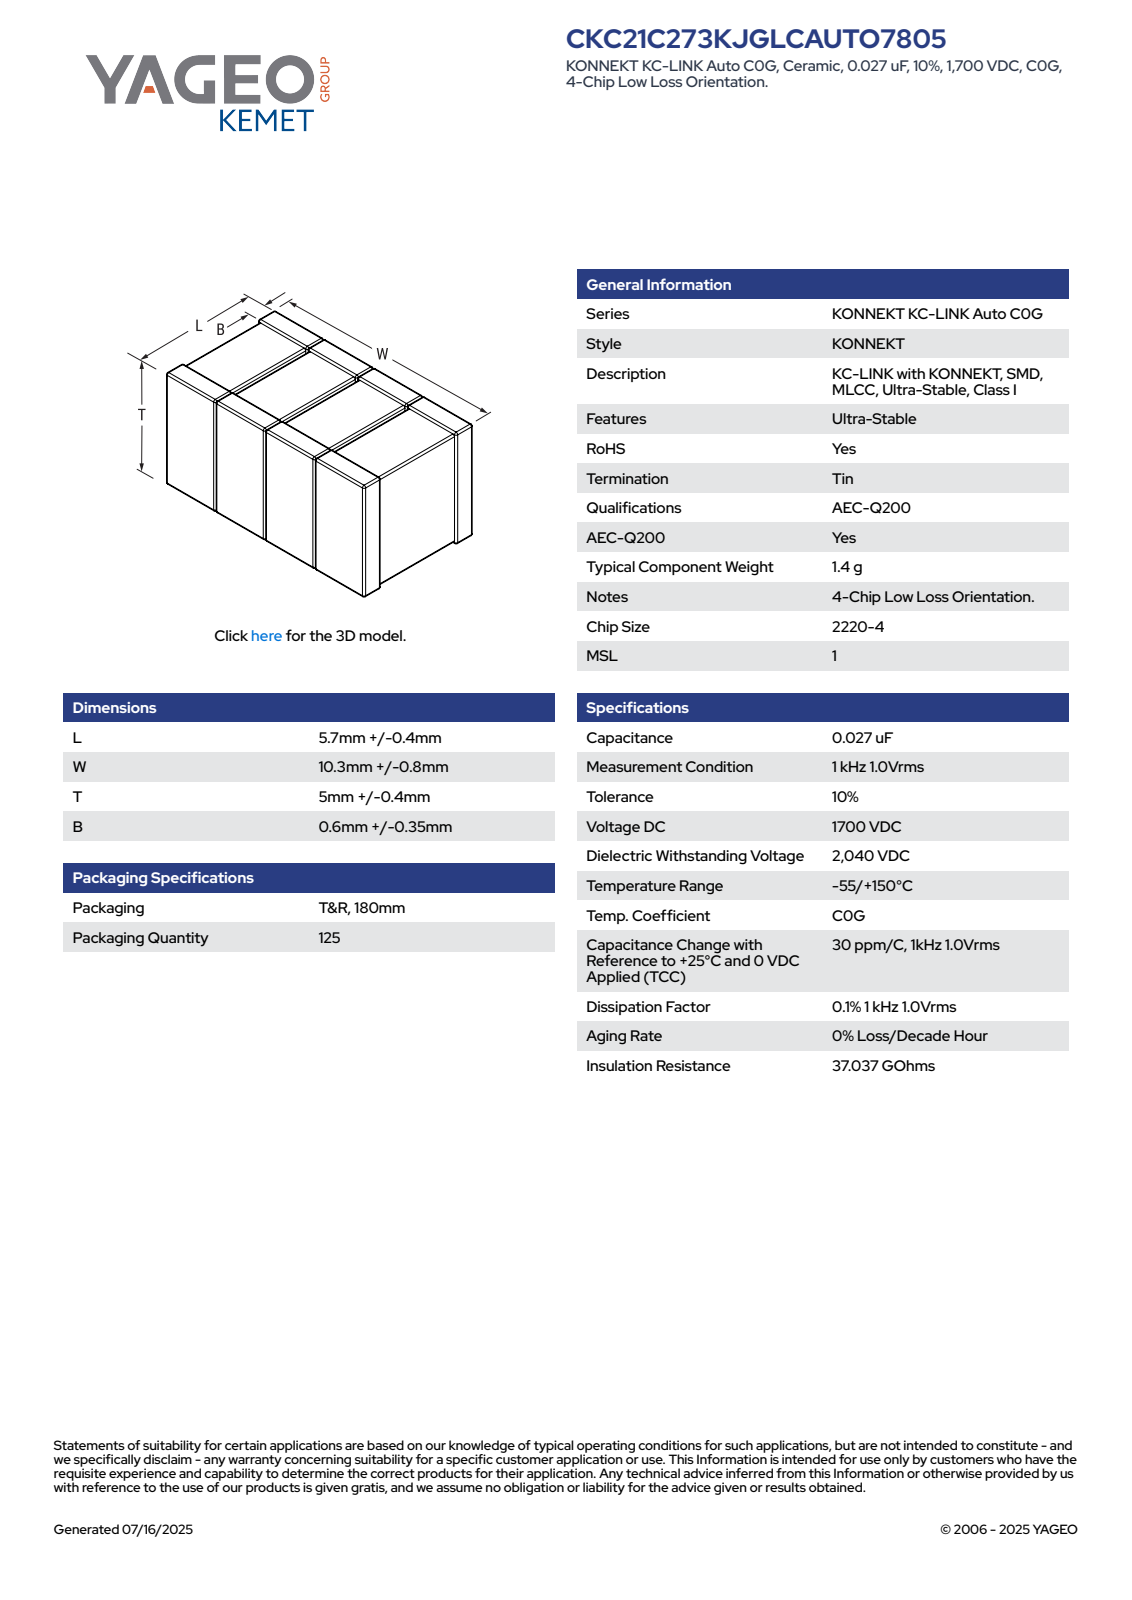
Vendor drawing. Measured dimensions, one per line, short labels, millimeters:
name: CCSS_K4LL_2220-4_L6.1W11.1B0.95T5.4
written by: SolidWorks 2021 (AUTOMOTIVE_DESIGN)
unit: mm
bodies: 16 solids, 468 faces (284 planar, 120 cylindrical, 64 other)
size: 11.1 × 6.1 × 5.4
volume: 341 mm³; area: 514 mm²
face distances: 2.77, 5.55, 2.6, 2.69, 2.78, 2.86, 5.46, 6.1, 8.32, 5.37
